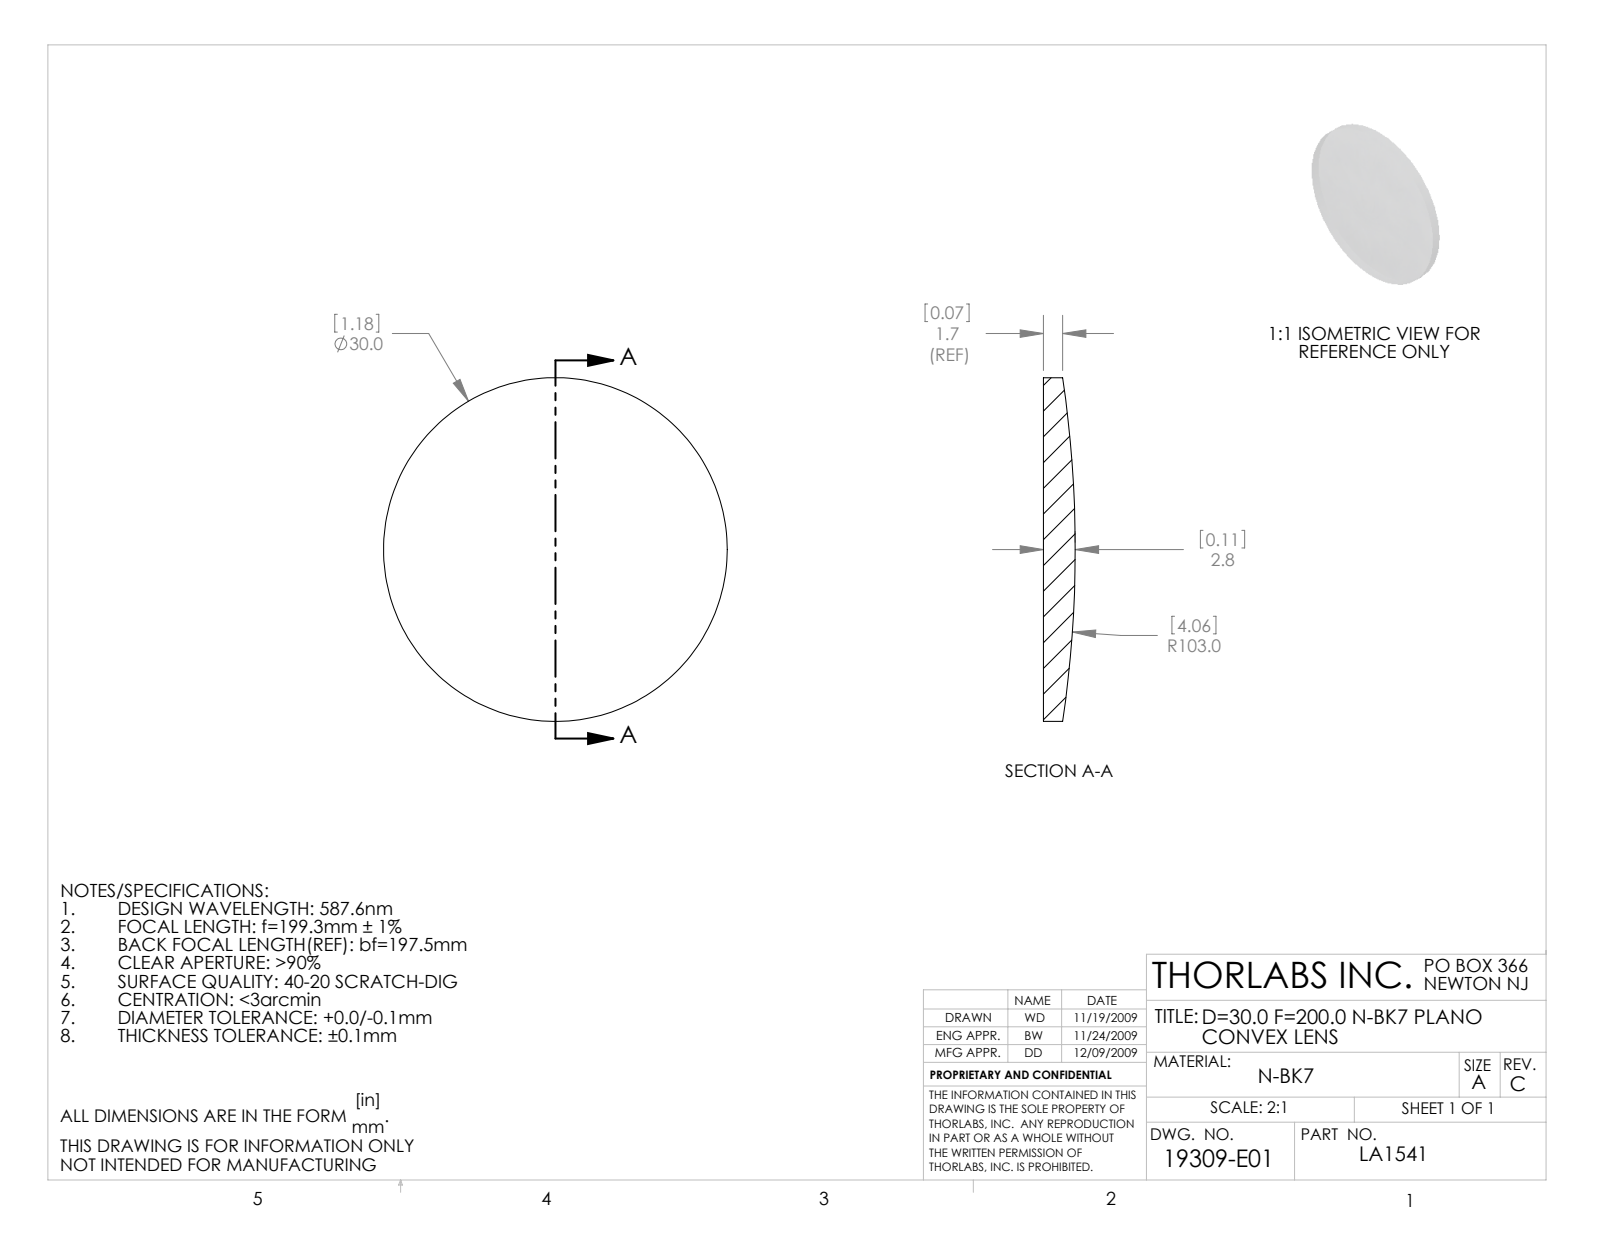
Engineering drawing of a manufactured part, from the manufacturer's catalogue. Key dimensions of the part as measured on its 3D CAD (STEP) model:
Part name (STEP PRODUCT): 19309-E0W
STEP written by: SolidWorks 2009 (AUTOMOTIVE_DESIGN)
Units: millimetres
Bodies: 1 solid, 5 faces (1 planar, 2 cylindrical, 2 other)
Overall size (bounding box): 30 × 30 × 2.78
Volume: 1 578 mm³ · Surface area: 1 576 mm²
Round bosses / shafts (diameter × count): ⌀30 ×1
